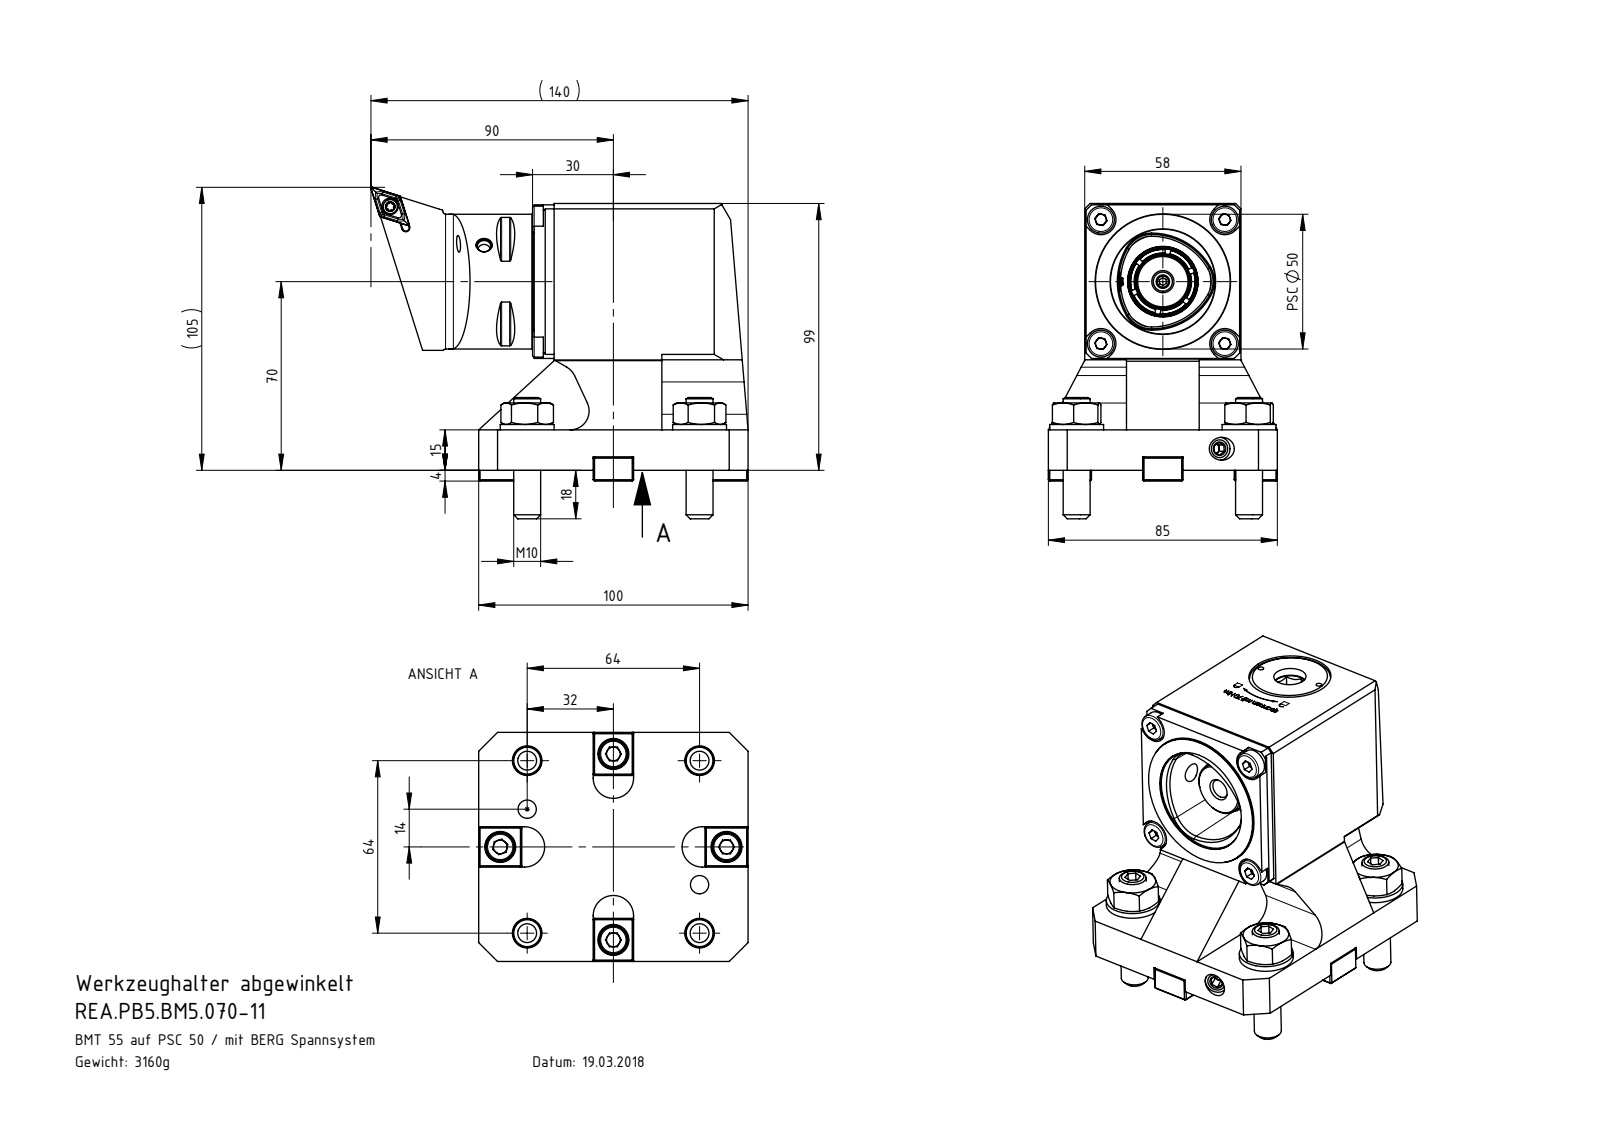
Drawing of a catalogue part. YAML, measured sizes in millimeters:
part_name: "765.18513.001.0.05; DIN 7984 - M6 x 16; 777.18513.002.1.01.01.01; REA.PB5.BM5.070-11 (+8 more)"
step_written_by: "SolidWorks 2017 (AUTOMOTIVE_DESIGN)"
units: millimeters
bodies: {solids: 51, faces: 1284, planar: 640, cylindrical: 251, other: 393}
overall_size: [117, 100, 85]
volume: 433929
surface_area: 135811
round_holes:
  - {diameter: 5, count: 8}
  - {diameter: 11, count: 8}
  - {diameter: 8.5, count: 5}
  - {diameter: 4.2, count: 4}
  - {diameter: 6.2, count: 4}
  - {diameter: 6.5, count: 4}
  - {diameter: 6.8, count: 4}
  - {diameter: 10.5, count: 4}
  - {diameter: 2.1, count: 3}
  - {diameter: 3, count: 3}
  - {diameter: 3.3, count: 2}
  - {diameter: 4, count: 2}
round_bosses_or_shafts:
  - {diameter: 10, count: 12}
  - {diameter: 6, count: 8}
  - {diameter: 20, count: 5}
  - {diameter: 8, count: 2}
  - {diameter: 7, count: 2}
  - {diameter: 4, count: 2}
  - {diameter: 50, count: 1}
  - {diameter: 49.7, count: 1}
partial_cylinders:
  - {radius: 0.3, count: 10}
  - {radius: 7, count: 6}
  - {radius: 5, count: 4}
  - {radius: 5.6, count: 4}
  - {radius: 7.5, count: 4}
  - {radius: 0.8, count: 3}
  - {radius: 0.2, count: 2}
  - {radius: 4, count: 2}
face_to_face_distances: [15, 58, 10, 20, 24, 99, 84, 48, 71.5, 13.5]
hole_center_spacings: [46, 32.1, 32.53, 33.53, 54.35, 64, 73.8, 80.62]
